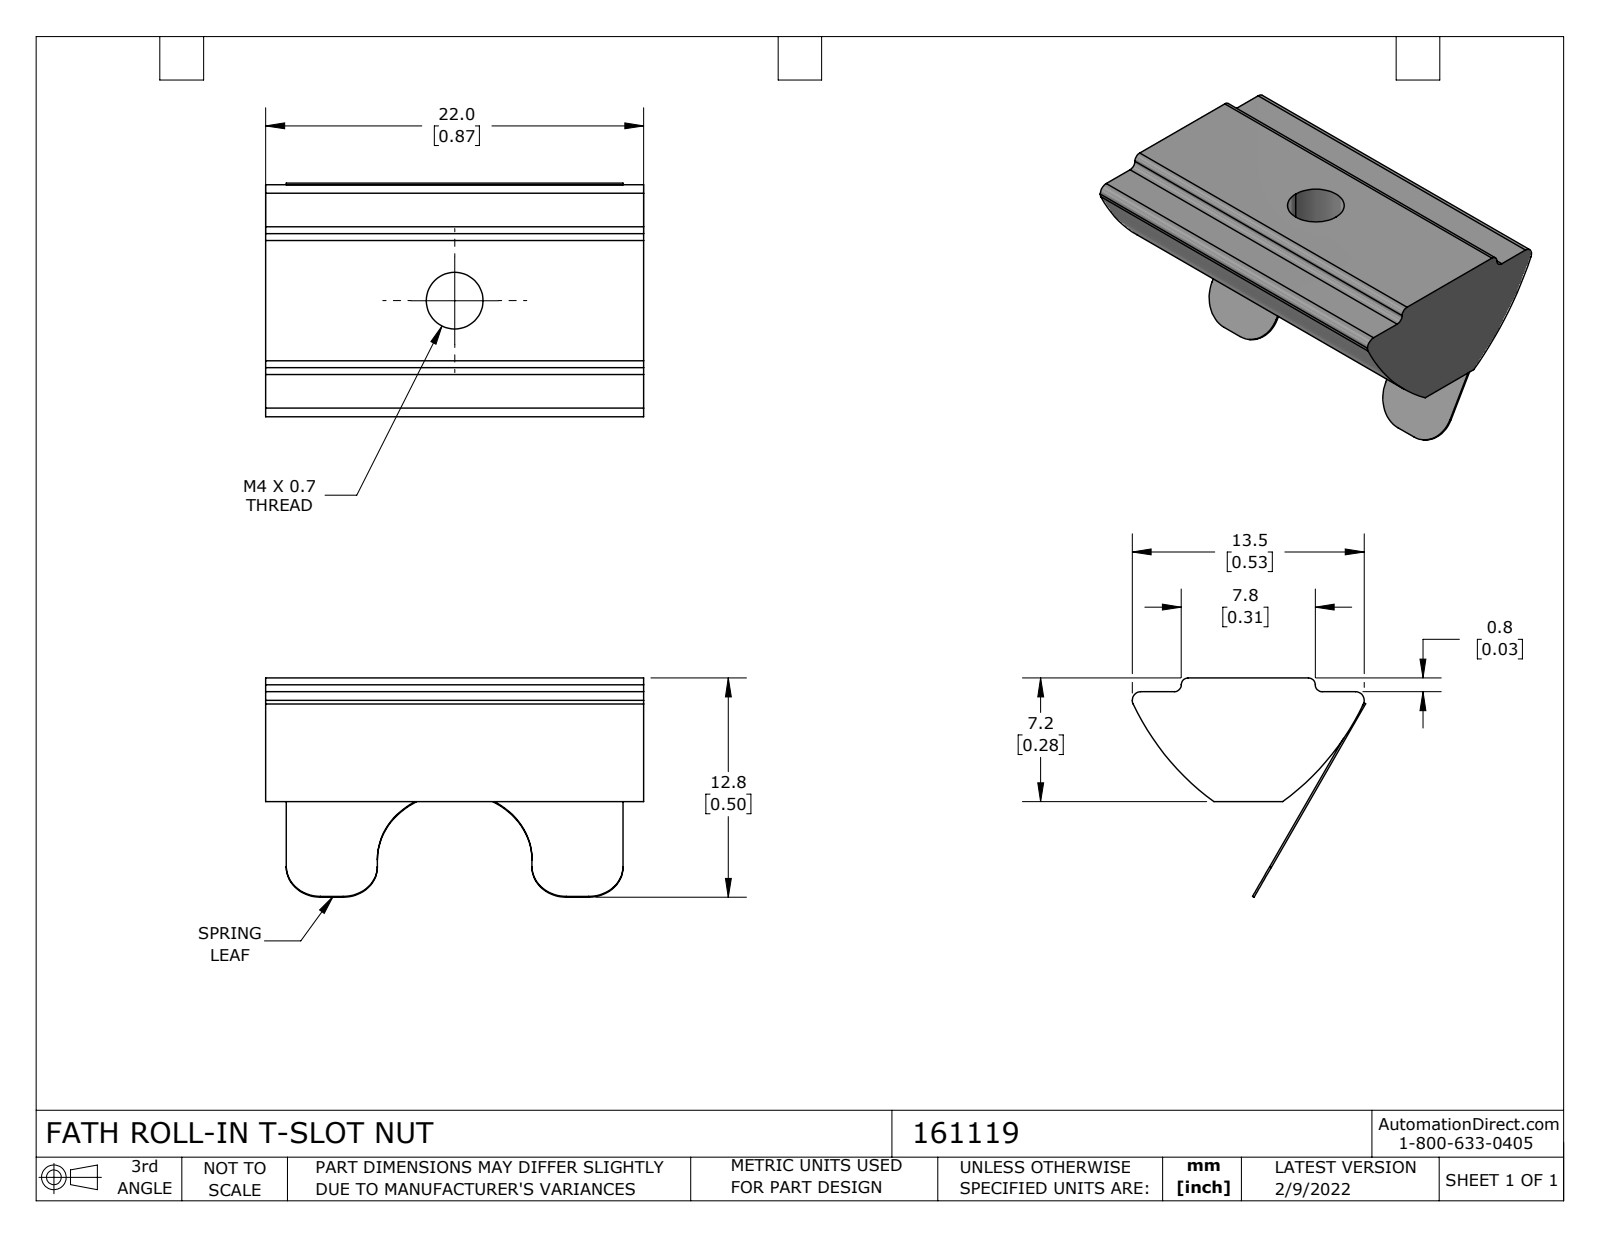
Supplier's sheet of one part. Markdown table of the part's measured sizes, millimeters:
| quantity | value |
| --- | --- |
| part name | 161119 |
| STEP written by | SolidWorks 2021 (CONFIG_CONTROL_DESIGN) |
| units | millimeters |
| bodies | 1 solid, 32 faces (16 planar, 16 cylindrical, 0 other) |
| overall size | 22 × 13.59 × 12.76 |
| volume | 1 492 mm³ |
| surface area | 1 268 mm² |
| round holes (diameter × count) | 3.3 × 1 |
| partial cylindrical surfaces (radius × count) | 0.4 × 4, 2 × 4, 0.5 × 2, 15 × 2, 4.5 × 1 |
| main face-to-face distances | 0.8, 6.4, 7.2, 22, 1.2, 20.8, 19.6, 13, 6.5, 15.5 |
